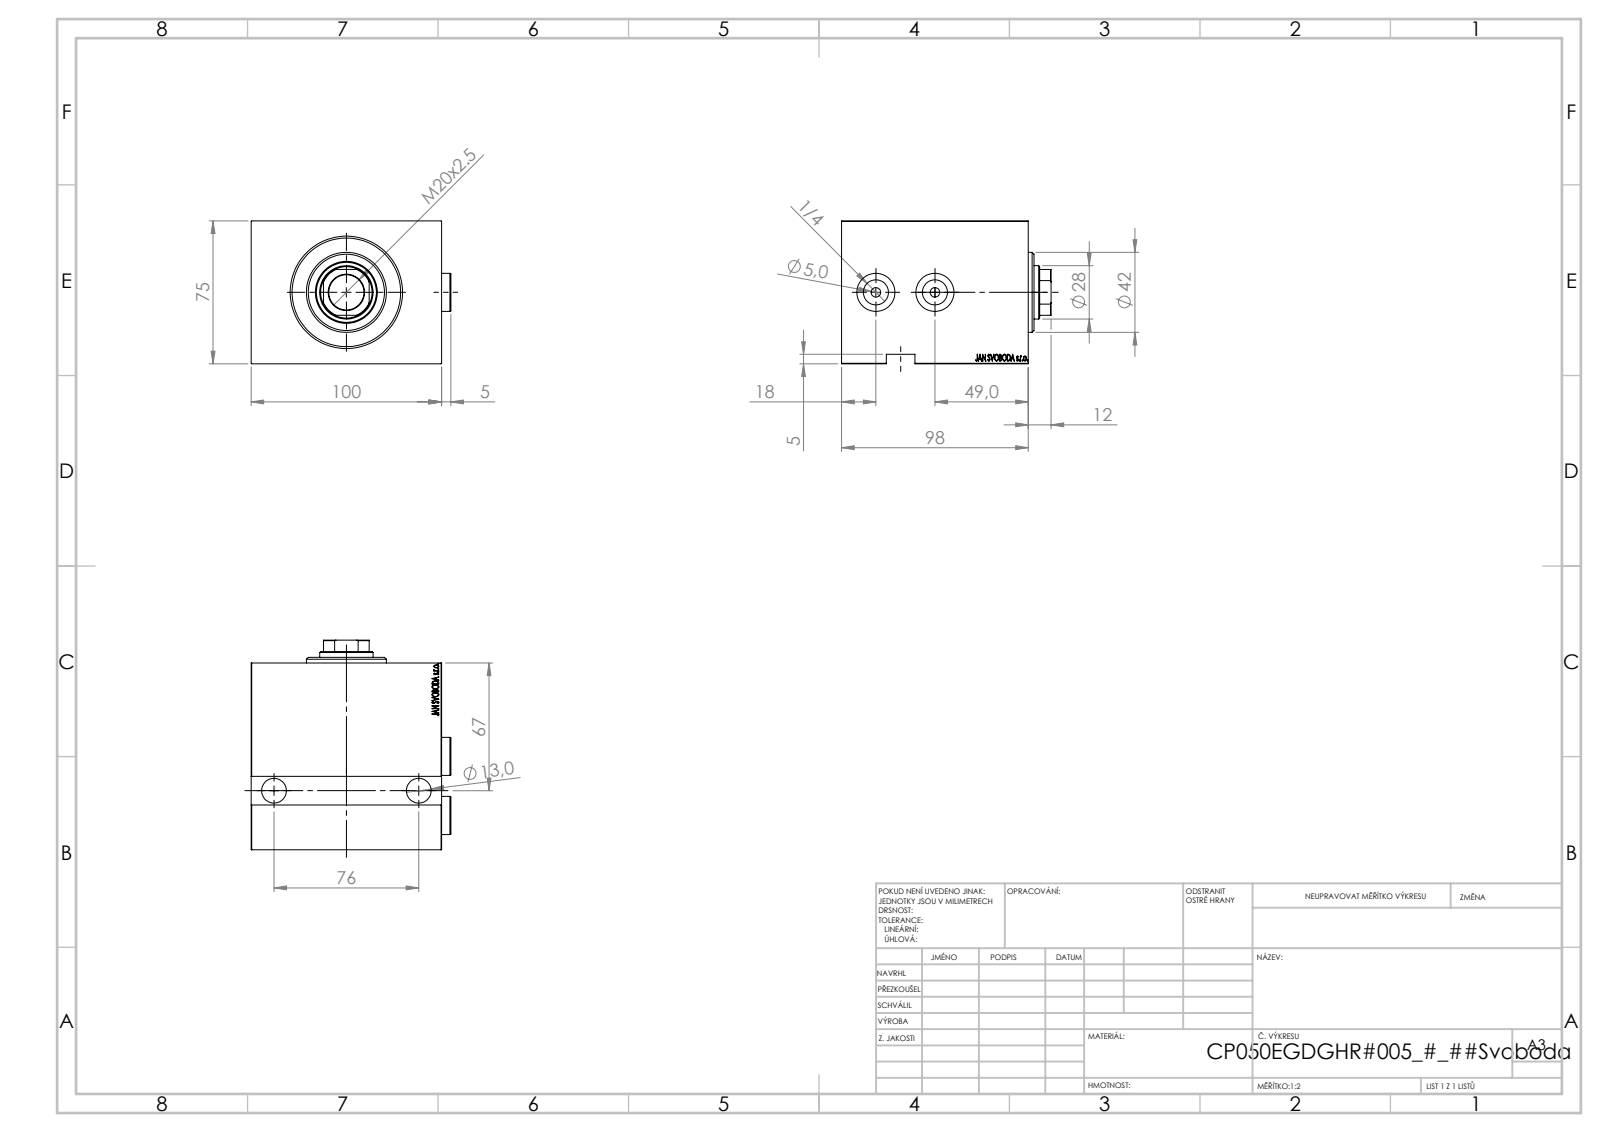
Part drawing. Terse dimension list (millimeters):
name: PLUG; V450CP_B_VCP; V450CP_E; V450CP_VC_B
written by: SolidWorks 2019 (CONFIG_CONTROL_DESIGN)
unit: mm
bodies: 5 solids, 928 faces (450 planar, 76 cylindrical, 402 other)
size: 110 × 104.9 × 75
volume: 690 433 mm³; area: 107 703 mm²
holes: 2× ⌀4, 2× ⌀5, 2× ⌀9.73, 2× ⌀13, 2× ⌀13.16, 2× ⌀15, 2× ⌀19, 2× ⌀20, 1× ⌀18.5, 1× ⌀28, 1× ⌀31.5, 1× ⌀32.5
bosses: 1× ⌀42
rounds: 1× R13.5
face distances: 75, 100, 98, 49, 14, 84, 5, 44, 35, 54
hole spacings: 31, 33.46, 42.55, 46.34, 64.49, 72.02, 76
